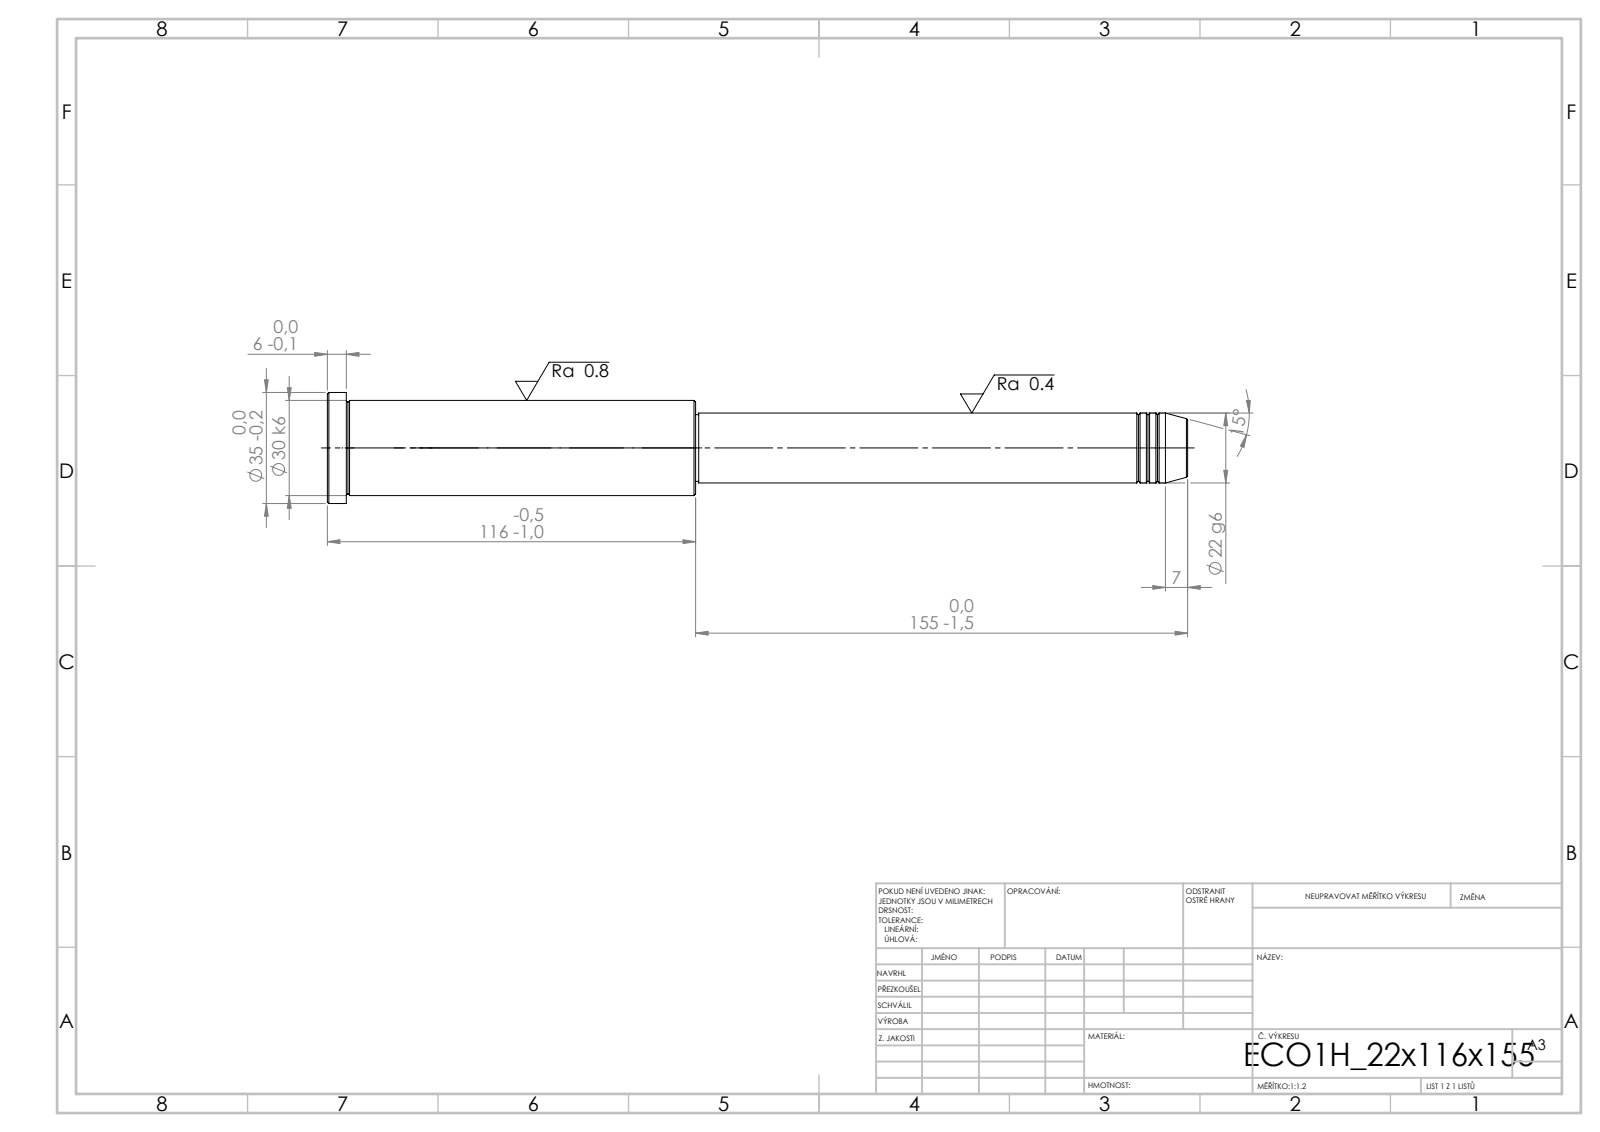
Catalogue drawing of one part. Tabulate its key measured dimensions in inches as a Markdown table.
| quantity | value |
| --- | --- |
| STEP written by | SolidWorks 2019 (CONFIG_CONTROL_DESIGN) |
| units | inches |
| bodies | 1 solid, 43 faces (5 planar, 14 cylindrical, 24 other) |
| overall size | 10.669 × 1.378 × 1.378 |
| volume | 8.656 in³ |
| surface area | 36.7 in² |
| round bosses / shafts (diameter × count) | 1.378 × 1, 1.181 × 1, 0.866 × 1, 0.827 × 1 |
| main face-to-face distances | 4.567, 4.331, 0.236, 6.102, 10.433, 10.669, 6.063, 0.039, 4.37, 4.606 |
